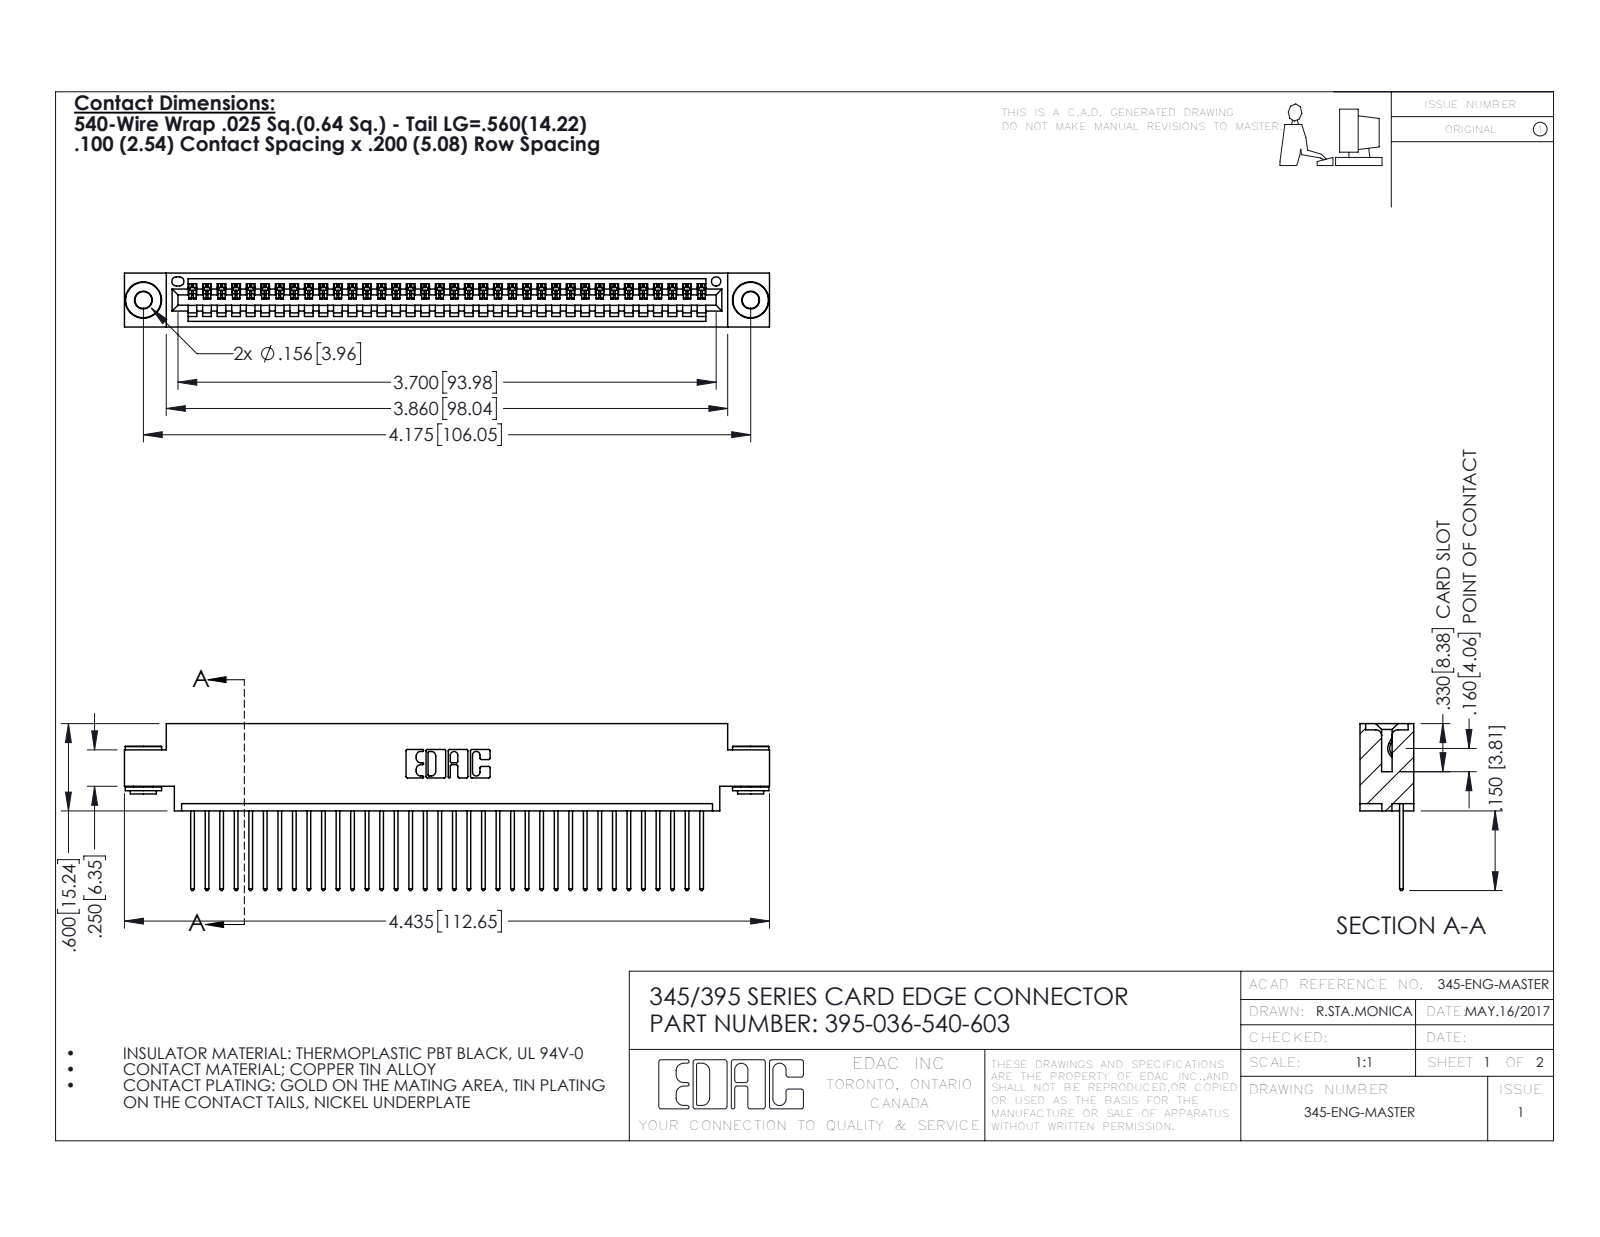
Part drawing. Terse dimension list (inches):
name: 345-292-001_345-293-140; 345-250-002_345-250-002-102; 395-036-540-603; 345 Part_0.170 Offset - 0.156 Dia-TH
written by: SolidWorks 2016 (CONFIG_CONTROL_DESIGN)
unit: in
bodies: 39 solids, 2256 faces (1534 planar, 714 cylindrical, 8 other)
size: 4.435 × 1.147 × 0.37
volume: 0.647 in³; area: 22.79 in²
holes: 2× ⌀0.116, 2× ⌀0.156, 1× ⌀0.064
bosses: 2× ⌀0.25, 2× ⌀0.18, 2× ⌀0.136
rounds: 72× R0.006, 72× R0.01, 22× R0.01, 6× R0.007, 6× R0.031, 3× R0.026, 2× R0.031, 2× R0.04
face distances: 0.072, 0.298, 0.37, 0.098, 0.272, 0.025, 0.2, 0.225, 0.175, 0.149
hole spacings: 0.27, 3.939, 4.175
